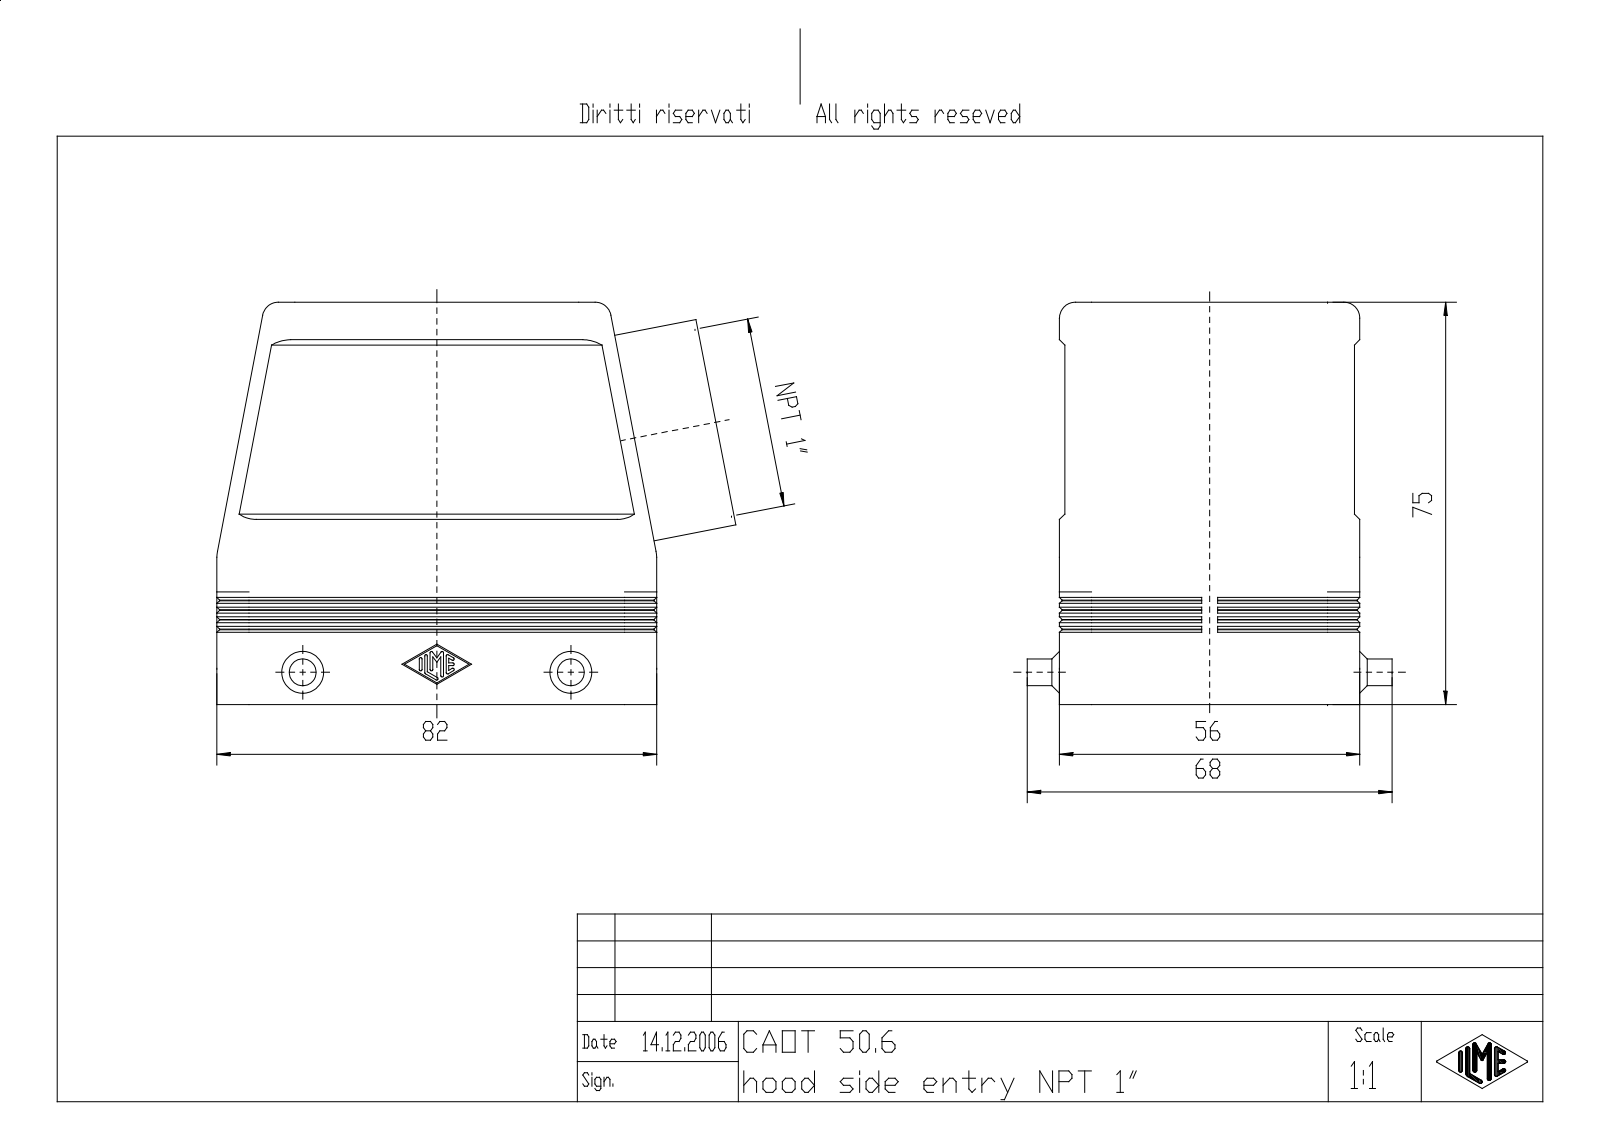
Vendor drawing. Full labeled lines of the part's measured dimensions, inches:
Part name (STEP PRODUCT): MSBO7675
STEP written by: Creo Elements/Direct Modeling 18.0B 02-Dec-2011 (C) Parametric Technology GmbH (AUTOMOTIVE_DESIGN)
Units: inches
Bodies: 1 solid, 373 faces (201 planar, 122 cylindrical, 50 other)
Overall size (bounding box): 3.809 × 2.953 × 2.677
Volume: 5.06 in³ · Surface area: 75.79 in²
Round holes (diameter × count): ⌀0.138 ×8, ⌀0.097 ×6, ⌀0.097 ×2
Round bosses / shafts (diameter × count): ⌀0.197 ×2, ⌀1.535 ×1
Partial cylindrical surfaces — rounded edges, fillets, slot ends (radius × count): R0.01 ×14, R0.236 ×10, R0.079 ×8, R0.118 ×8, R0.217 ×4, R0.768 ×2
Main face-to-face distances: 0.118, 2.087, 1.969, 0.079, 2.165, 0.039, 2.047, 2.205, 2.126, 0.443
Hole centre spacings: 0.63, 0.945, 2.598, 2.674, 2.765, 0.315, 1.575, 2.617
